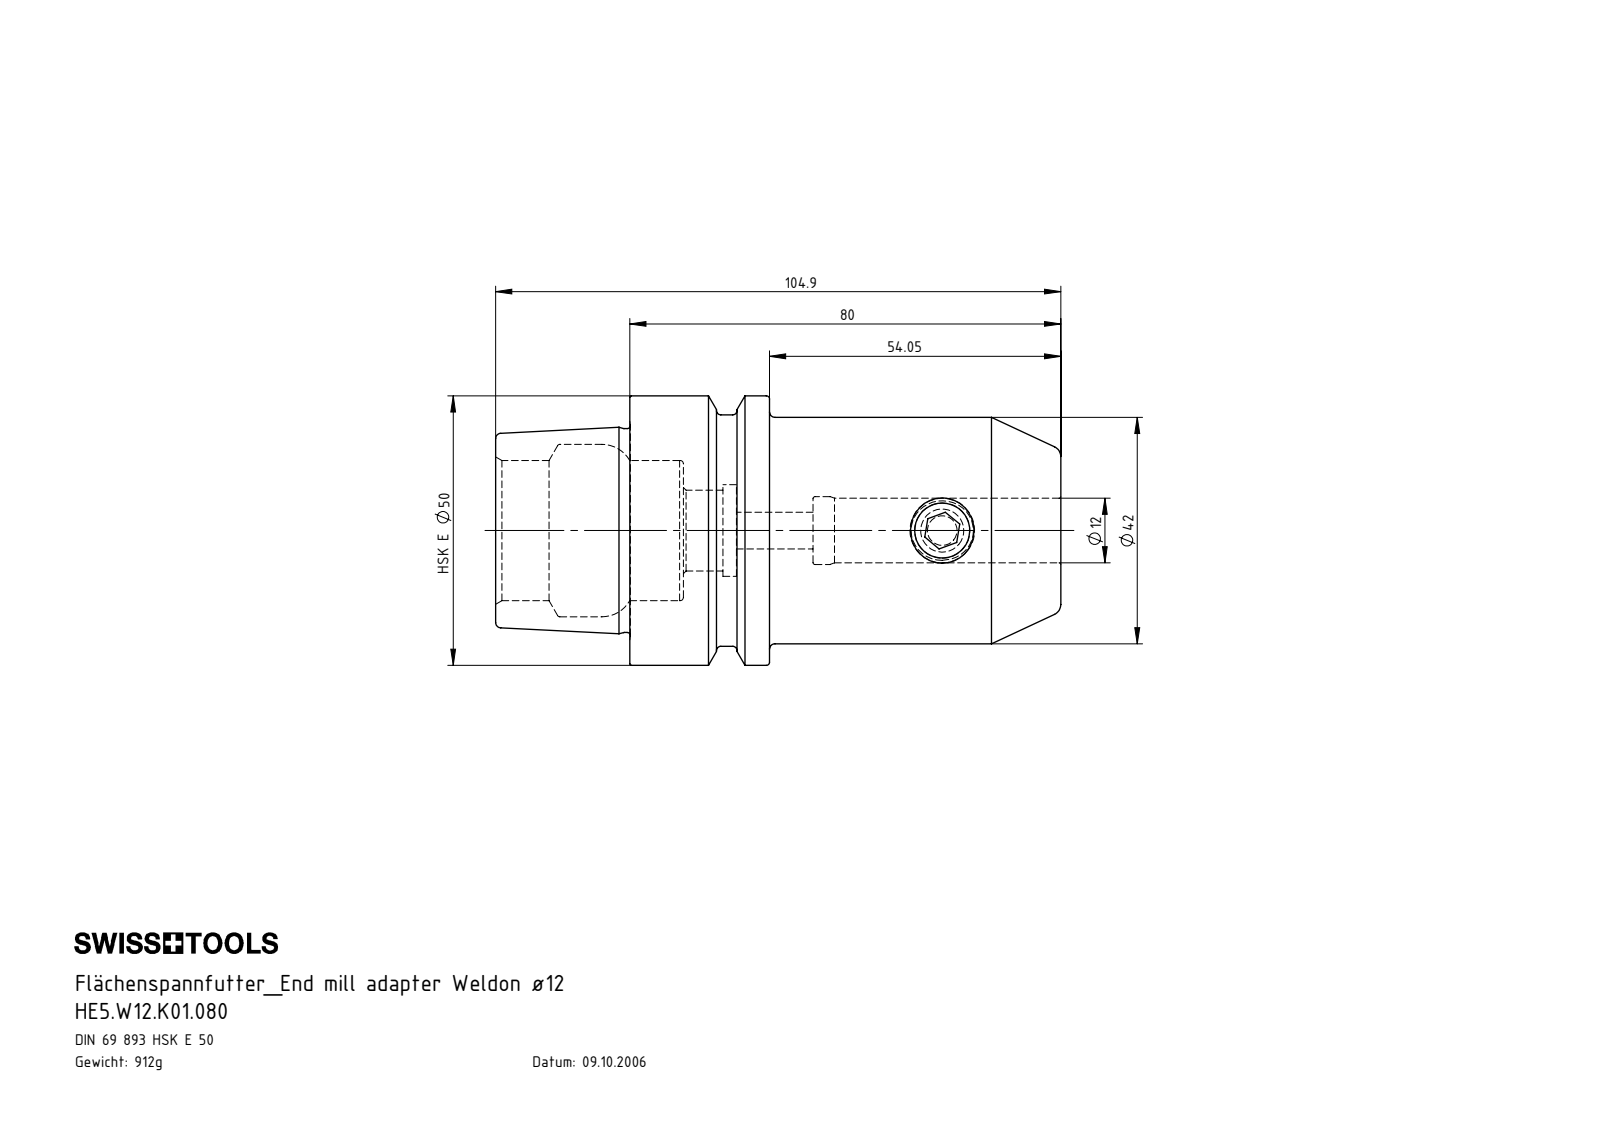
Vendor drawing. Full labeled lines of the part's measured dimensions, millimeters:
Part name (STEP PRODUCT): HE5-W12.K01.080_B_Fertigbearbeitung; HE5.W12.K01.080; W12-ER1.001.016
STEP written by: SolidWorks 2017 (AUTOMOTIVE_DESIGN)
Units: millimetres
Bodies: 2 solids, 109 faces (19 planar, 30 cylindrical, 60 other)
Overall size (bounding box): 104.9 × 50 × 50
Volume: 116 193 mm³ · Surface area: 24 614 mm²
Round holes (diameter × count): ⌀6.8 ×1, ⌀10.25 ×1, ⌀12 ×1, ⌀12.6 ×1, ⌀15 ×1, ⌀17 ×1, ⌀26 ×1, ⌀32 ×1
Round bosses / shafts (diameter × count): ⌀50 ×1, ⌀42.95 ×1, ⌀42 ×1, ⌀37.81 ×1, ⌀12 ×1
Main face-to-face distances: 80, 25.95, 54.05, 24.9, 50.85, 104.9, 34.85, 9.95, 16, 70.05
